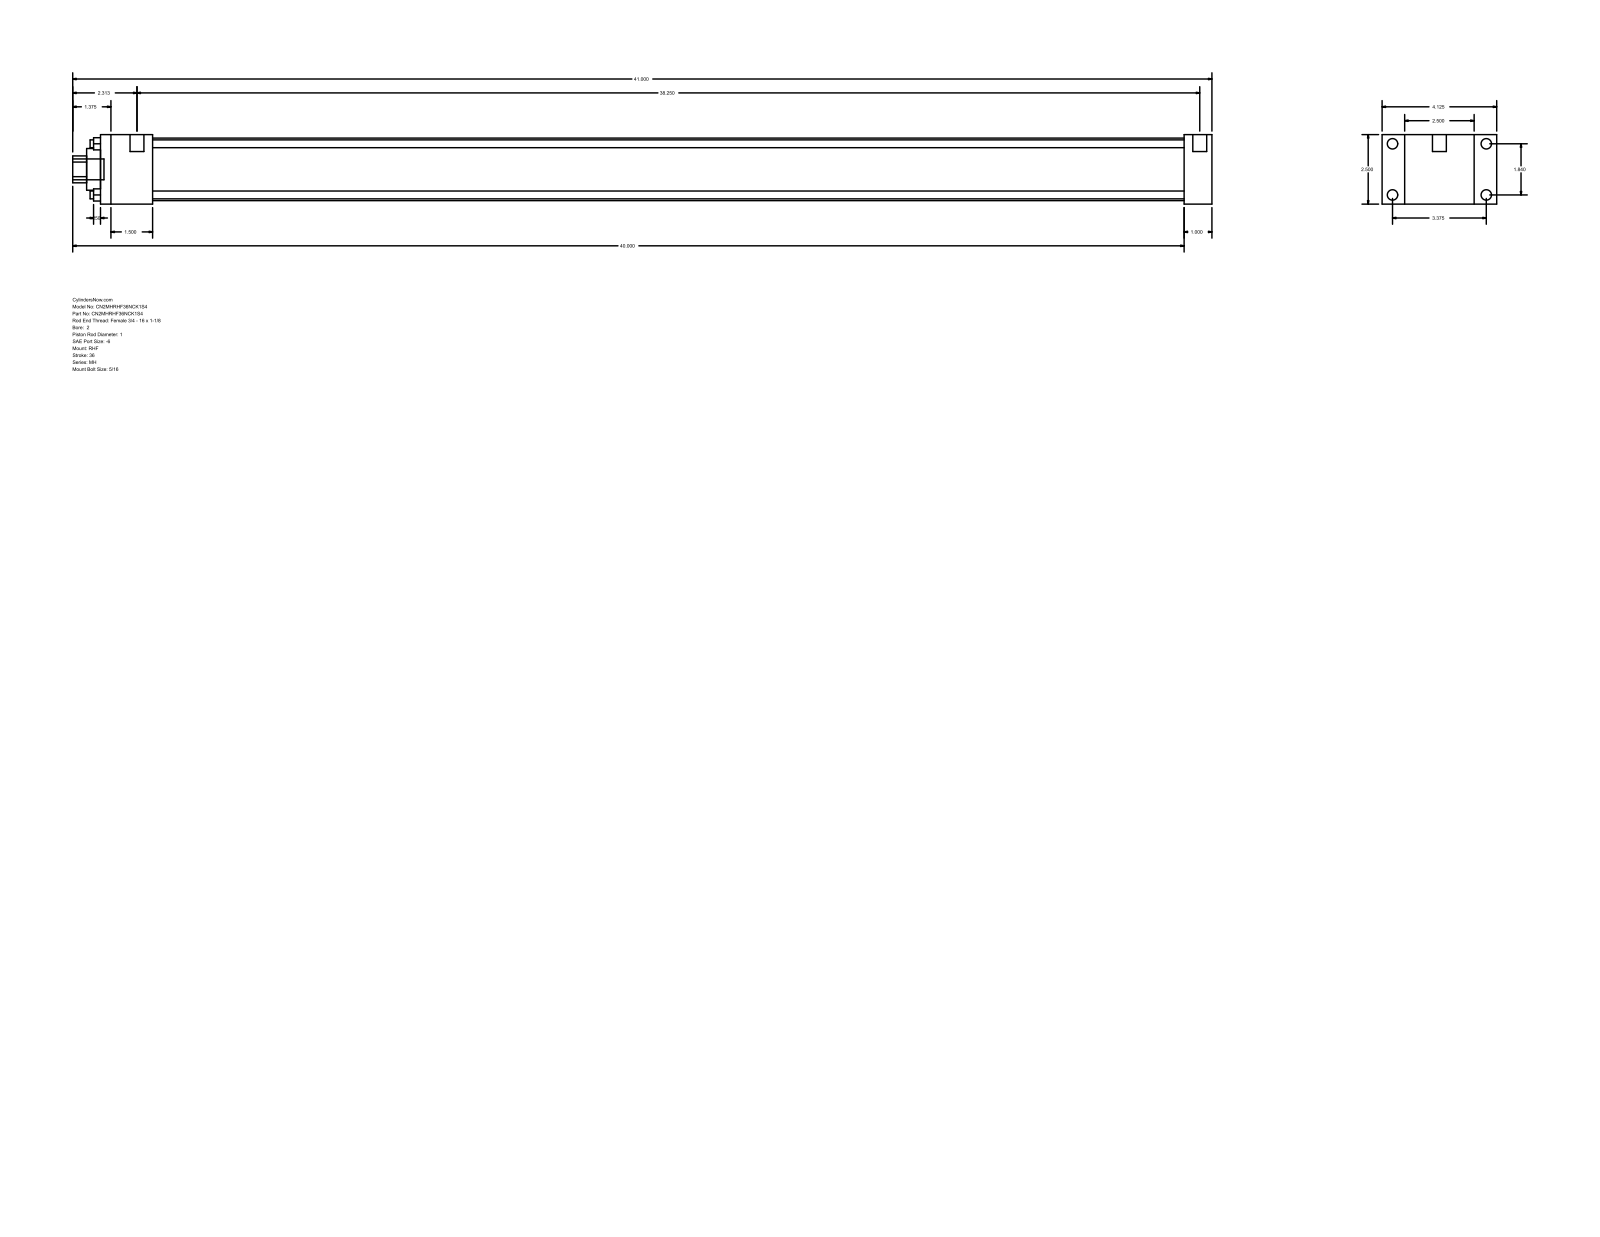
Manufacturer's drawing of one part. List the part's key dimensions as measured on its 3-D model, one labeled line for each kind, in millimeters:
Part name (STEP PRODUCT): MH_RHF__0200_1
STEP written by: GSSL Pune (CONFIG_CONTROL_DESIGN)
Units: millimetres
Bodies: 0 solids, 88 faces (60 planar, 28 cylindrical, 0 other)
Overall size (bounding box): 1041.4 × 104.78 × 63.5
Round holes (diameter × count): ⌀7.14 ×4, ⌀25.4 ×1, ⌀38.1 ×1, ⌀57.15 ×1
Round bosses / shafts (diameter × count): ⌀9.53 ×4, ⌀5.56 ×4, ⌀12.7 ×2, ⌀19.05 ×1
Partial cylindrical surfaces — rounded edges, fillets, slot ends (radius × count): R12.29 ×1
Main face-to-face distances: 63.5, 25.4, 20.64, 84.14, 1016, 990.6, 104.78, 47.63, 942.97, 968.37
Hole centre spacings: 33.05, 46.74, 66.1
